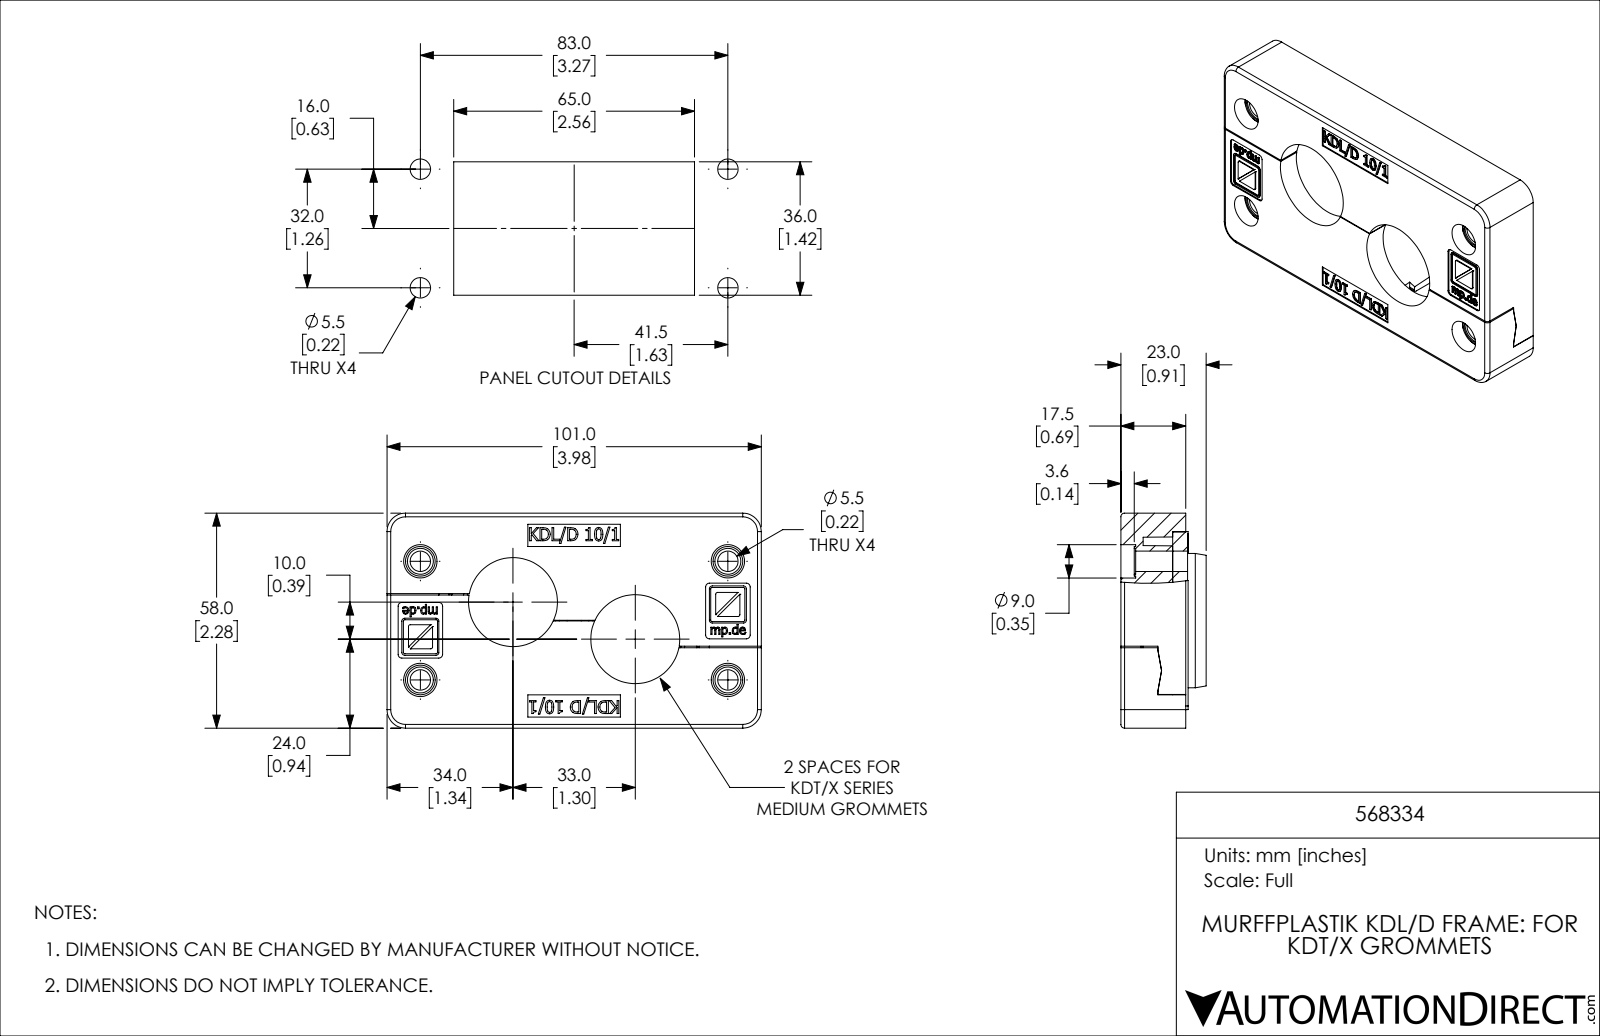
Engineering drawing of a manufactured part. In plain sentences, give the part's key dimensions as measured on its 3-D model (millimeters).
The part is named "568334". Its 3-D file was written by "SolidWorks 2019 (CONFIG_CONTROL_DESIGN)". It is 3 solids with 1045 faces: 573 planar, 193 cylindrical and 279 other. Overall it measures 101 by 58 by 23 millimeters. Its volume is 81 660 cubic millimeters and its surface area 41 390 square millimeters. Round holes: 4 of diameter 5, 4 of diameter 5.5, 4 of diameter 7, 4 of diameter 9, 2 of diameter 6, 2 of diameter 24, 2 of diameter 24.9. Round bosses or shafts: 4 of diameter 8. Partial cylindrical surfaces (rounded edges, fillets, slot ends): 46 of radius 1, 15 of radius 0.5, 12 of radius 0.4, 8 of radius 0.8, 4 of radius 0.1, 4 of radius 0.2, 4 of radius 0.3, 4 of radius 5. The main face-to-face distances are 5, 53, 14, 4, 3.5, 6, 8, 12, 18, 0.5. The hole center spacings are 7.7, 9.9, 11, 14.4, 17.6, 21, 22.1, 25.6.
